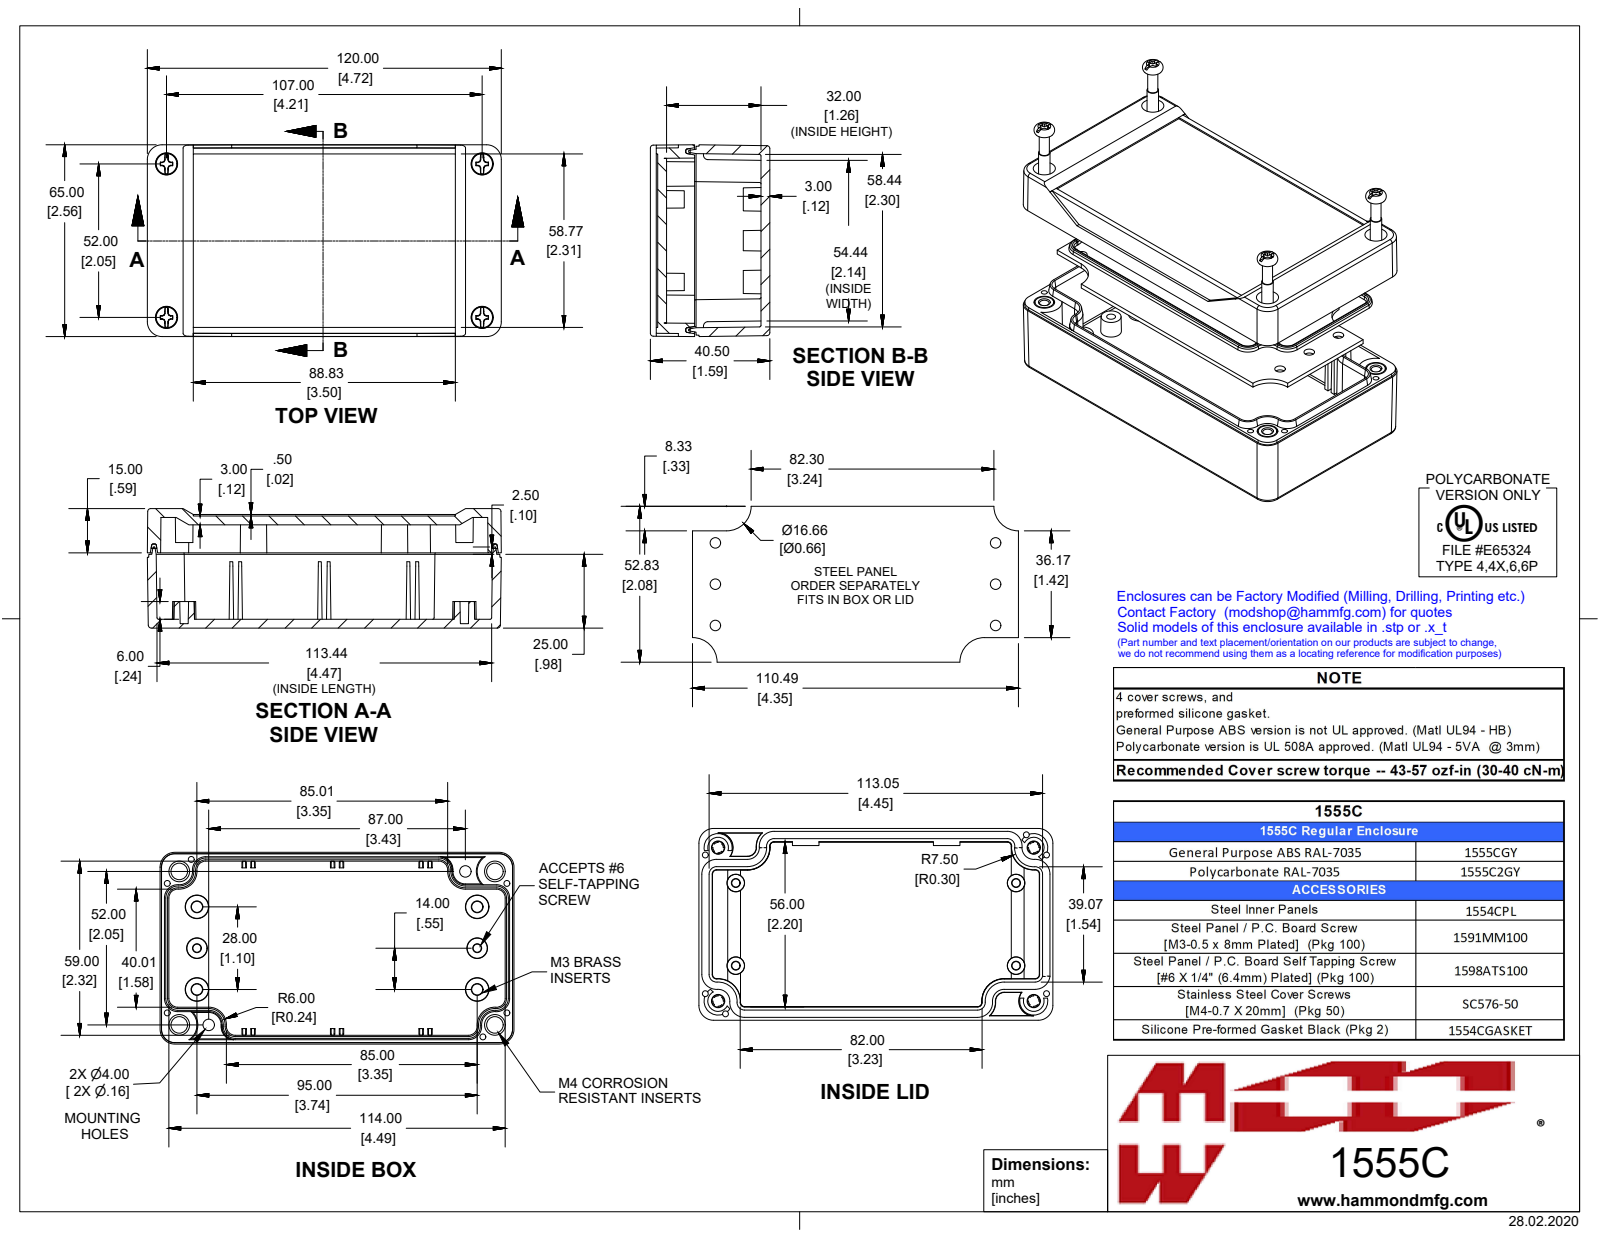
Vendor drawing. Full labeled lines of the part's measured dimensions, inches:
Part name (STEP PRODUCT): 1555C2GY
STEP written by: SolidWorks 2019 (AUTOMOTIVE_DESIGN)
Units: inches
Bodies: 15 solids, 1394 faces (428 planar, 358 cylindrical, 608 other)
Overall size (bounding box): 4.724 × 2.559 × 1.594
Volume: 5.832 in³ · Surface area: 113 in²
Round holes (diameter × count): ⌀0.079 ×12, ⌀0.097 ×4, ⌀0.128 ×4, ⌀0.276 ×4
Round bosses / shafts (diameter × count): ⌀0.25 ×4, ⌀0.218 ×4, ⌀0.21 ×4, ⌀0.19 ×4, ⌀0.154 ×4, ⌀0.153 ×4, ⌀0.15 ×4, ⌀0.135 ×4
Partial cylindrical surfaces — rounded edges, fillets, slot ends (radius × count): R0.02 ×24, R0.039 ×8, R0.197 ×8, R0.055 ×4, R0.069 ×4, R0.082 ×4, R0.187 ×4, R0.059 ×2
Main face-to-face distances: 0.118, 1.378, 1.496, 1.26, 0.059, 0.177, 0.02, 0.138, 0.098, 0.374
Hole centre spacings: 0.197, 0.226, 0.42, 1.956, 4.384, 4.684, 4.797, 0.062
